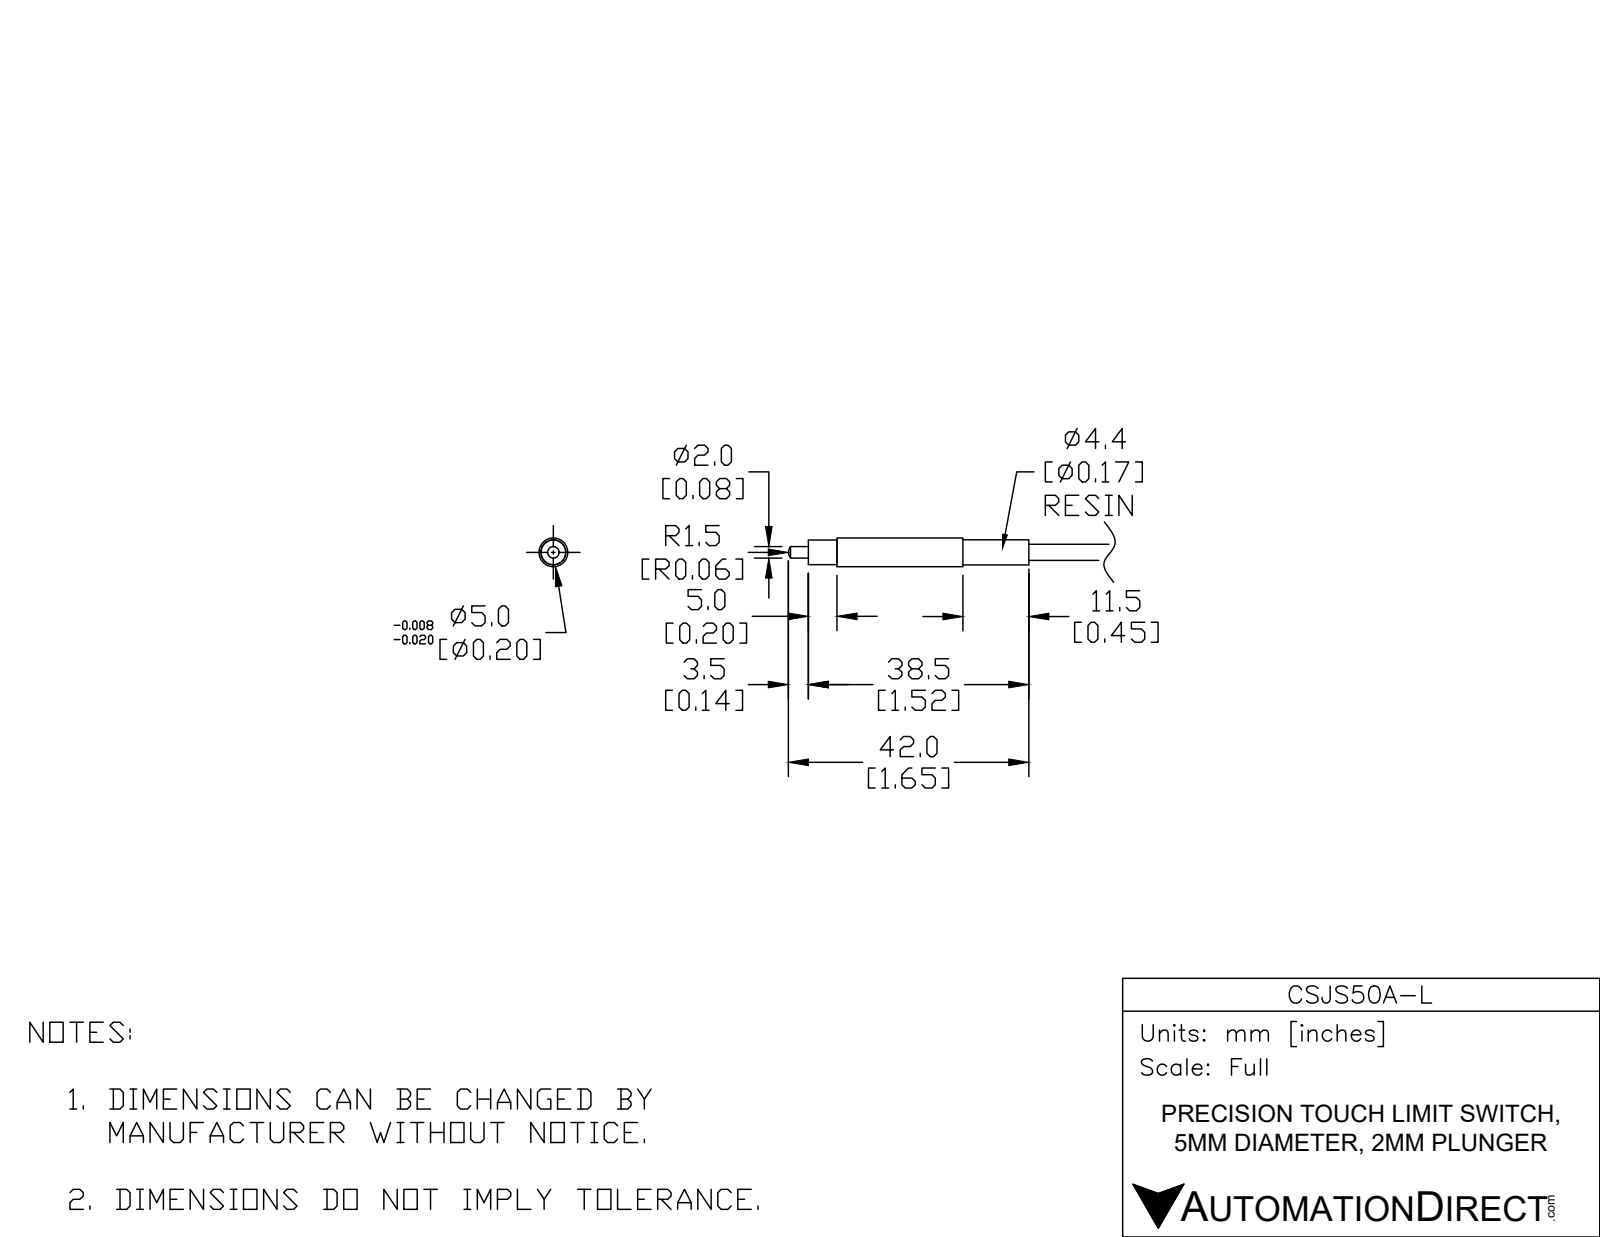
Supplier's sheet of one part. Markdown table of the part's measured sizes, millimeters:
| quantity | value |
| --- | --- |
| part name | CSJS50A-L |
| STEP written by | SolidWorks 2017 (AUTOMOTIVE_DESIGN) |
| units | millimeters |
| bodies | 1 solid, 17 faces (5 planar, 10 cylindrical, 2 other) |
| overall size | 56 × 5 × 5 |
| volume | 770 mm³ |
| surface area | 755 mm² |
| round bosses / shafts (diameter × count) | 5 × 1, 4.4 × 1, 4.3 × 1, 2.8 × 1, 2 × 1 |
| main face-to-face distances | 38.5, 52.5, 14, 5, 33.5, 47.5, 27, 22, 11.5, 25.5 |
